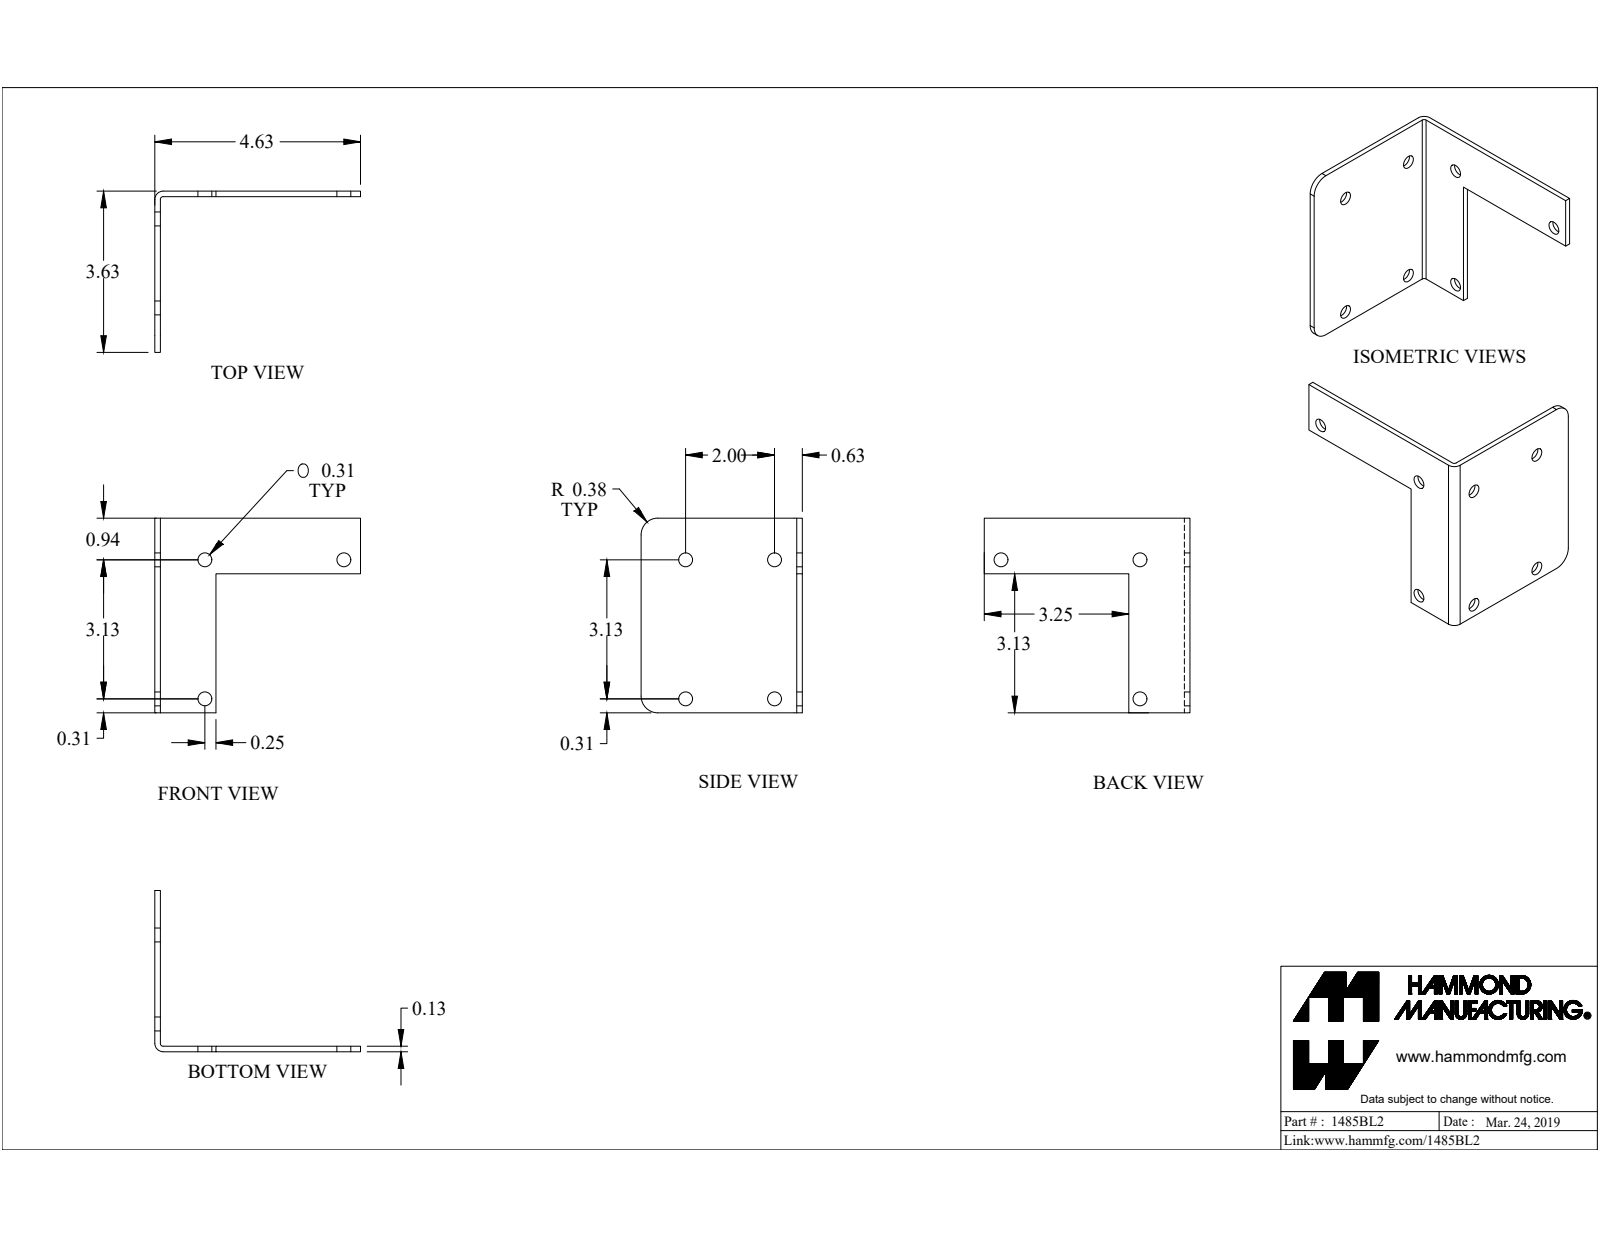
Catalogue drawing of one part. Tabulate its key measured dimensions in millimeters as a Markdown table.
| quantity | value |
| --- | --- |
| part name | 1485BL2 |
| STEP written by | SolidWorks 2019 (CONFIG_CONTROL_DESIGN) |
| units | millimeters |
| bodies | 1 solid, 21 faces (10 planar, 11 cylindrical, 0 other) |
| overall size | 117.5 × 111.1 × 92.1 |
| volume | 50 310 mm³ |
| surface area | 34 230 mm² |
| round holes (diameter × count) | 8 × 7 |
| partial cylindrical surfaces (radius × count) | 9.5 × 2, 1.5 × 1, 4.7 × 1 |
| main face-to-face distances | 3.2, 111.1, 88.9, 92.1, 31.8, 79.4, 34.9, 31.8, 117.5, 114.3 |
| hole center spacings | 79.4, 50.8, 94.2, 112.3 |
